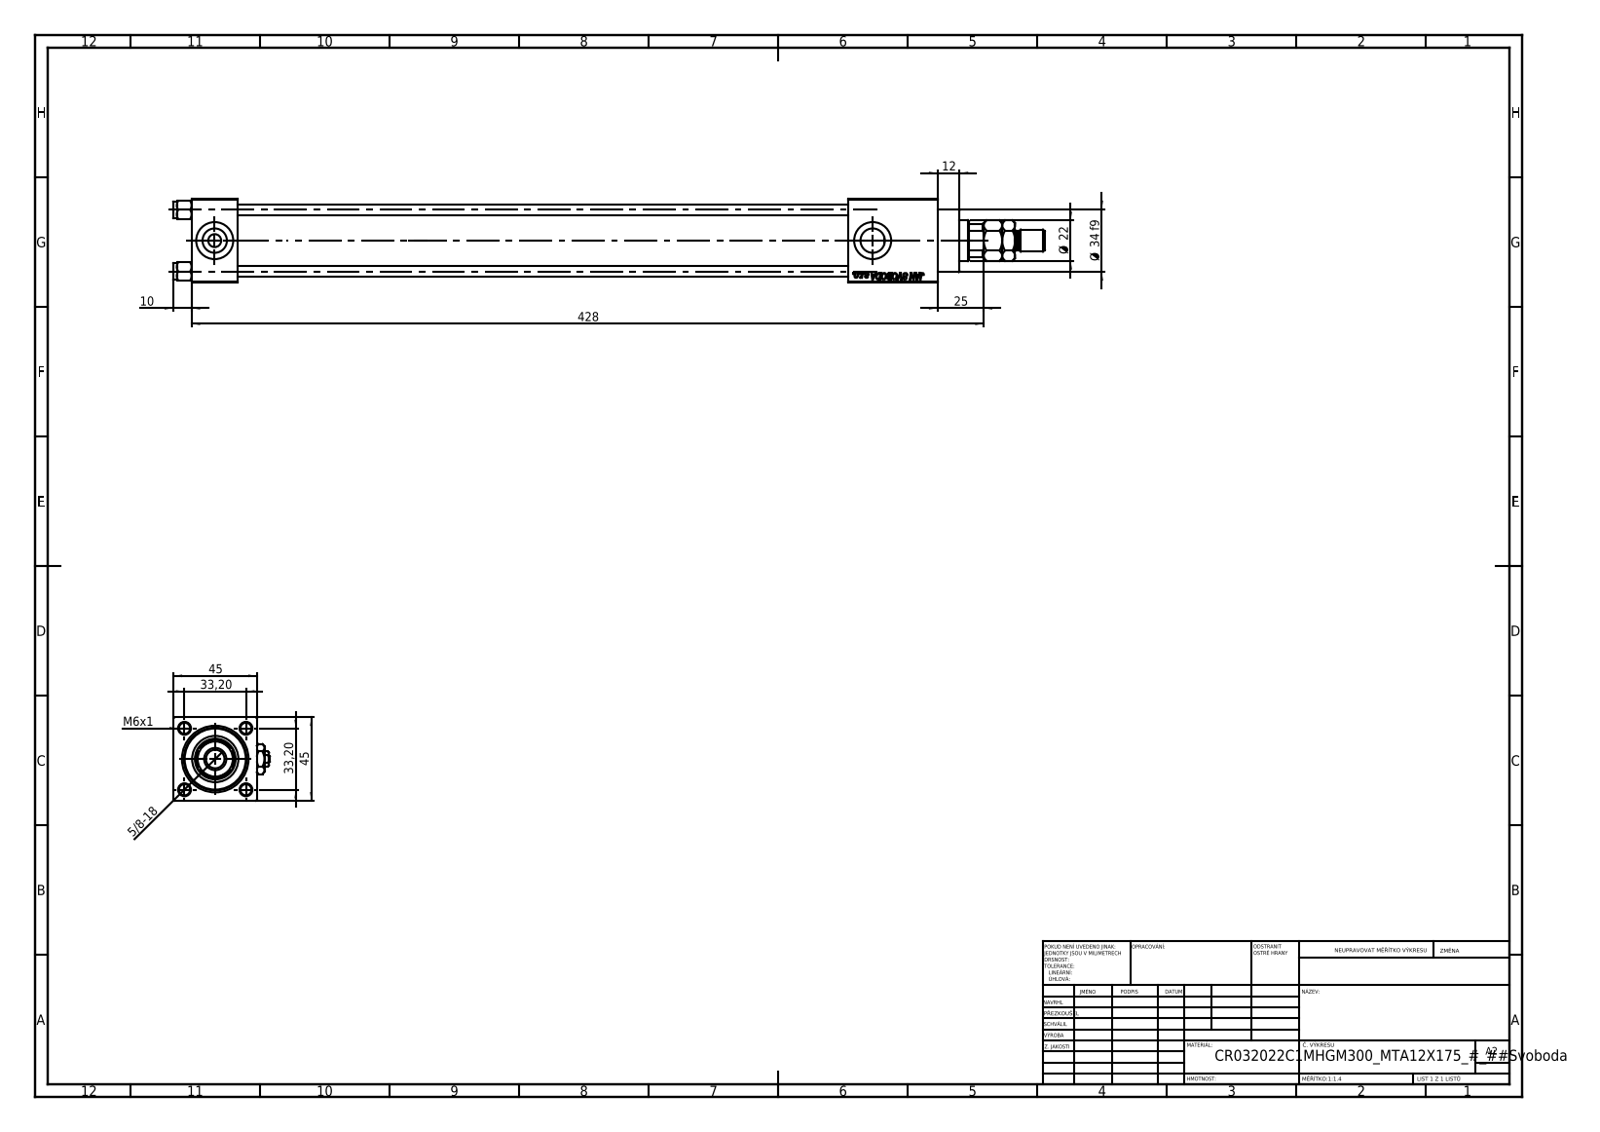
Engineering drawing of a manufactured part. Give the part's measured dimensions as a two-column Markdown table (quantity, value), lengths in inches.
| quantity | value |
| --- | --- |
| part name | V215CR_C_TYCINKA; NUT_M5_C; V215CR_C_Body; V215_VC_A (+3 more) |
| STEP written by | SolidWorks 2019 (CONFIG_CONTROL_DESIGN) |
| units | inches |
| bodies | 13 solids, 1244 faces (564 planar, 94 cylindrical, 586 other) |
| overall size | 18.543 × 2.047 × 1.772 |
| volume | 27.25 in³ |
| surface area | 273.5 in² |
| round holes (diameter × count) | 0.236 × 4, 0.276 × 2, 0.518 × 2, 0.787 × 2, 0.413 × 1, 0.866 × 1, 0.945 × 1, 0.984 × 1, 1.26 × 1, 1.299 × 1 |
| round bosses / shafts (diameter × count) | 0.354 × 4, 1.496 × 1, 1.339 × 1, 0.472 × 1, 0.394 × 1 |
| partial cylindrical surfaces (radius × count) | 0.413 × 1 |
| main face-to-face distances | 1.772, 0.984, 15.866, 13.976, 12.992, 14.882, 0.512, 1.89, 14.736, 13.752 |
| hole center spacings | 0.924, 1.307, 1.848, 13.996 |
